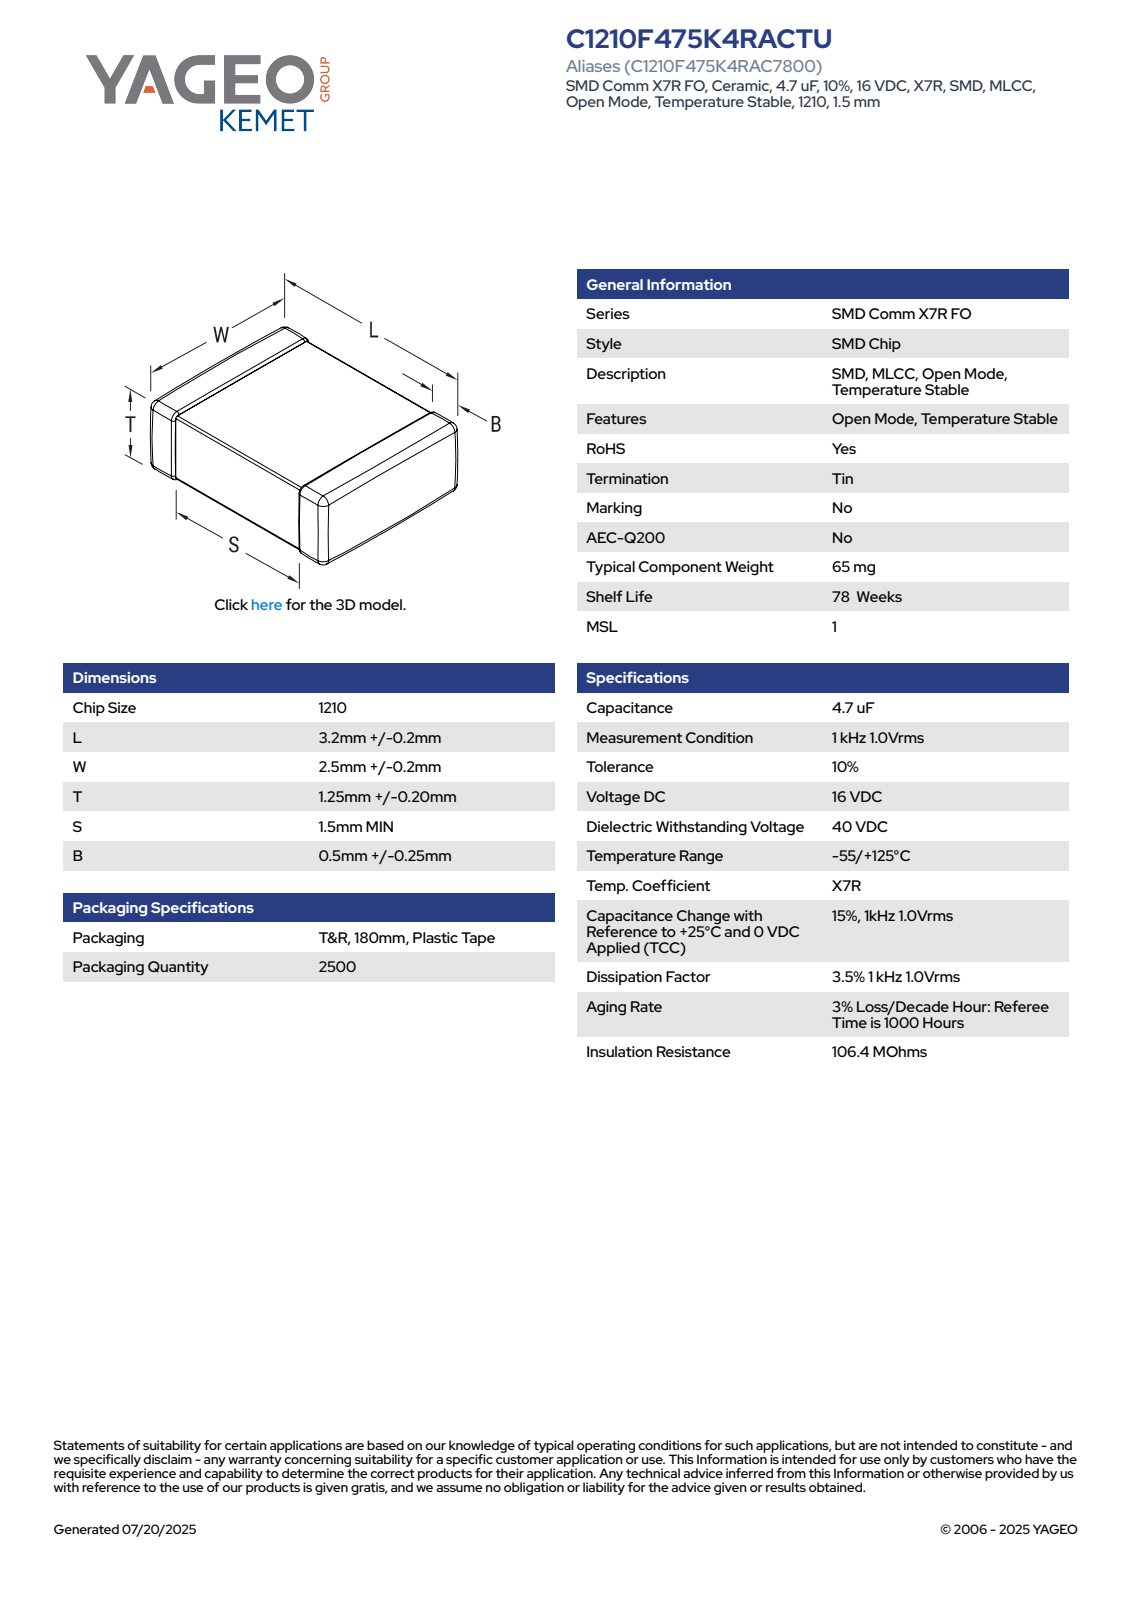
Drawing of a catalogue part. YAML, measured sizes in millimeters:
part_name: "CCS_CCSTDNOS_1210_L3.4W2.7T1.45B0.75"
step_written_by: "SolidWorks 2014 (AUTOMOTIVE_DESIGN)"
units: millimeters
bodies: {solids: 4, faces: 125, planar: 71, cylindrical: 38, other: 16}
overall_size: [3.4, 2.7, 1.45]
volume: 12
surface_area: 35
face_to_face_distances: [1.39, 1.33, 3.4, 2.64, 1.45, 2.58, 2.7, 1.4, 1.34, 1.31]
